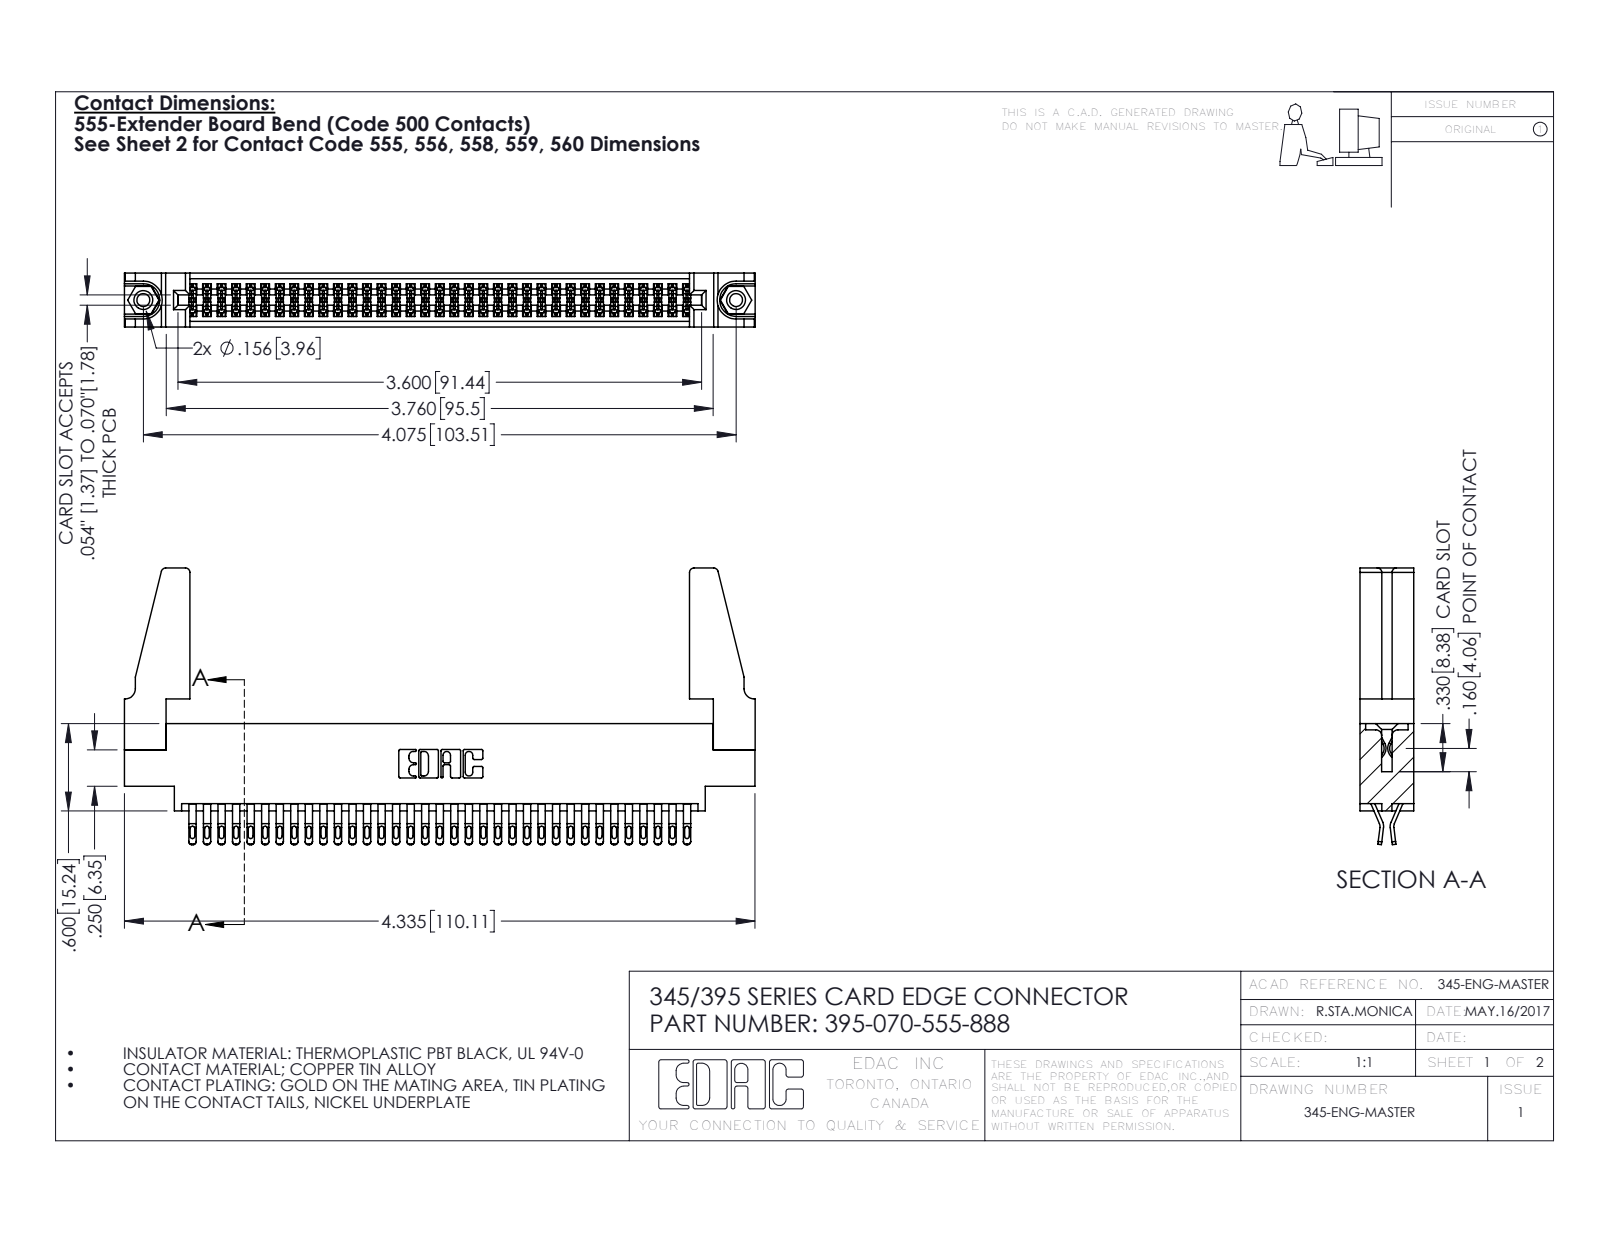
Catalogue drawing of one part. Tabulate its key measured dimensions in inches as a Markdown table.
| quantity | value |
| --- | --- |
| part name | 345-220-078_345-220-088; 395-070-555-888; 345-292-001_555 Tail; 345 Part_0.170 Offset - 0.156 Dia-TH (+1 more) |
| STEP written by | SolidWorks 2016 (CONFIG_CONTROL_DESIGN) |
| units | inches |
| bodies | 75 solids, 4174 faces (2326 planar, 1832 cylindrical, 16 other) |
| overall size | 4.336 × 1.902 × 0.37 |
| volume | 0.853 in³ |
| surface area | 30.51 in² |
| round holes (diameter × count) | 0.089 × 2, 0.125 × 2, 0.156 × 2, 0.064 × 1 |
| round bosses / shafts (diameter × count) | 0.155 × 2 |
| partial cylindrical surfaces (radius × count) | 0.016 × 175, 0.02 × 140, 0.006 × 105, 0.01 × 22, 0.03 × 8, 0.007 × 6, 0.031 × 6, 0.026 × 3 |
| main face-to-face distances | 0.072, 0.37, 0.298, 0.025, 0.098, 0.272, 0.2, 0.225, 0.175, 0.149 |
| hole center spacings | 0.27, 3.839, 4.075 |
